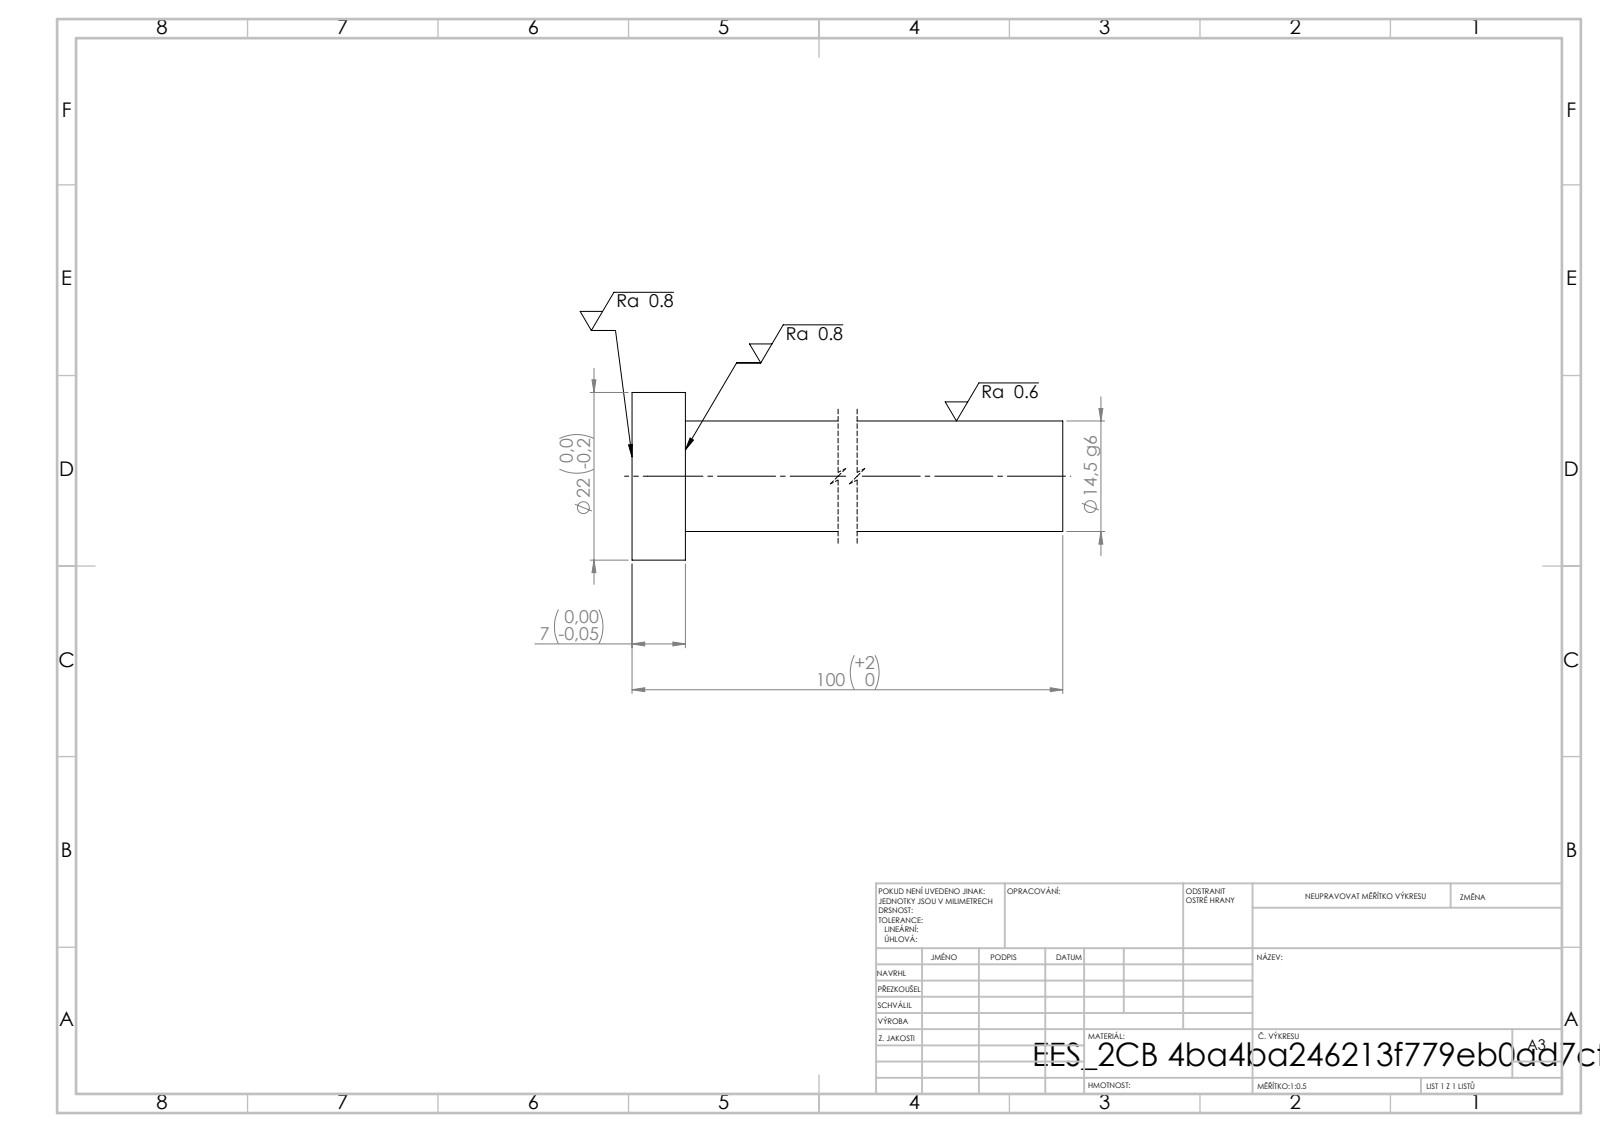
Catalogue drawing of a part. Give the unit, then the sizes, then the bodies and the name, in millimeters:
Units: millimetres
Overall size (bounding box): 100 × 22 × 22
Round bosses / shafts (diameter × count): ⌀22 ×1, ⌀14.5 ×1
Main face-to-face distances: 7, 100, 93
Volume: 18 018 mm³ · Surface area: 5 481 mm²
Bodies: 1 solid, 7 faces (3 planar, 4 cylindrical, 0 other)
STEP written by: SolidWorks 2019 (CONFIG_CONTROL_DESIGN)
